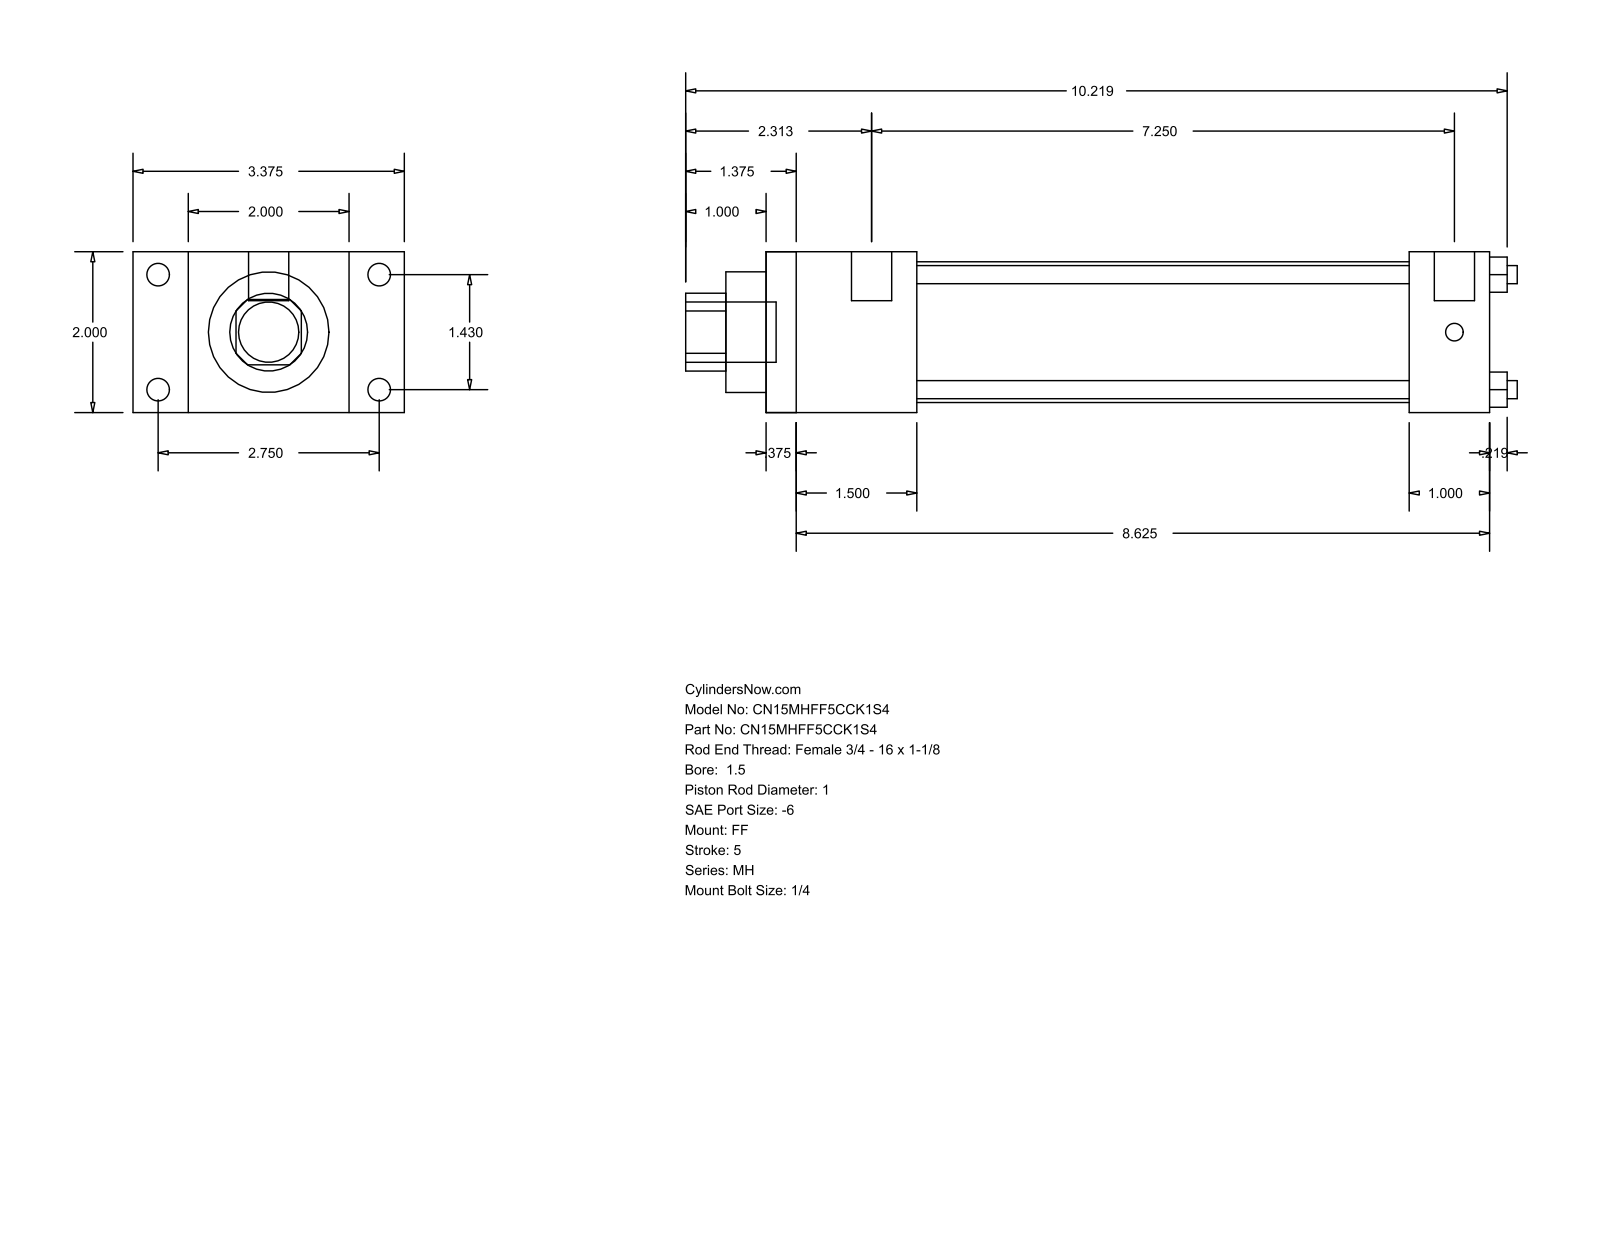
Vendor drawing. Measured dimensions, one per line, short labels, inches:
name: MH_FF__0150_1
written by: GSSL Pune (CONFIG_CONTROL_DESIGN)
unit: in
bodies: 0 solids, 92 faces (64 planar, 28 cylindrical, 0 other)
size: 10.344 × 3.375 × 2
holes: 4× ⌀0.225, 1× ⌀1, 1× ⌀1.5, 1× ⌀1.75
bosses: 4× ⌀0.281, 4× ⌀0.219, 2× ⌀0.5, 1× ⌀0.75
rounds: 1× R0.484
face distances: 2, 9, 0.375, 8.625, 1, 0.687, 2.687, 1.875, 1.5, 7.125
hole spacings: 1.011, 1.43, 2.022
